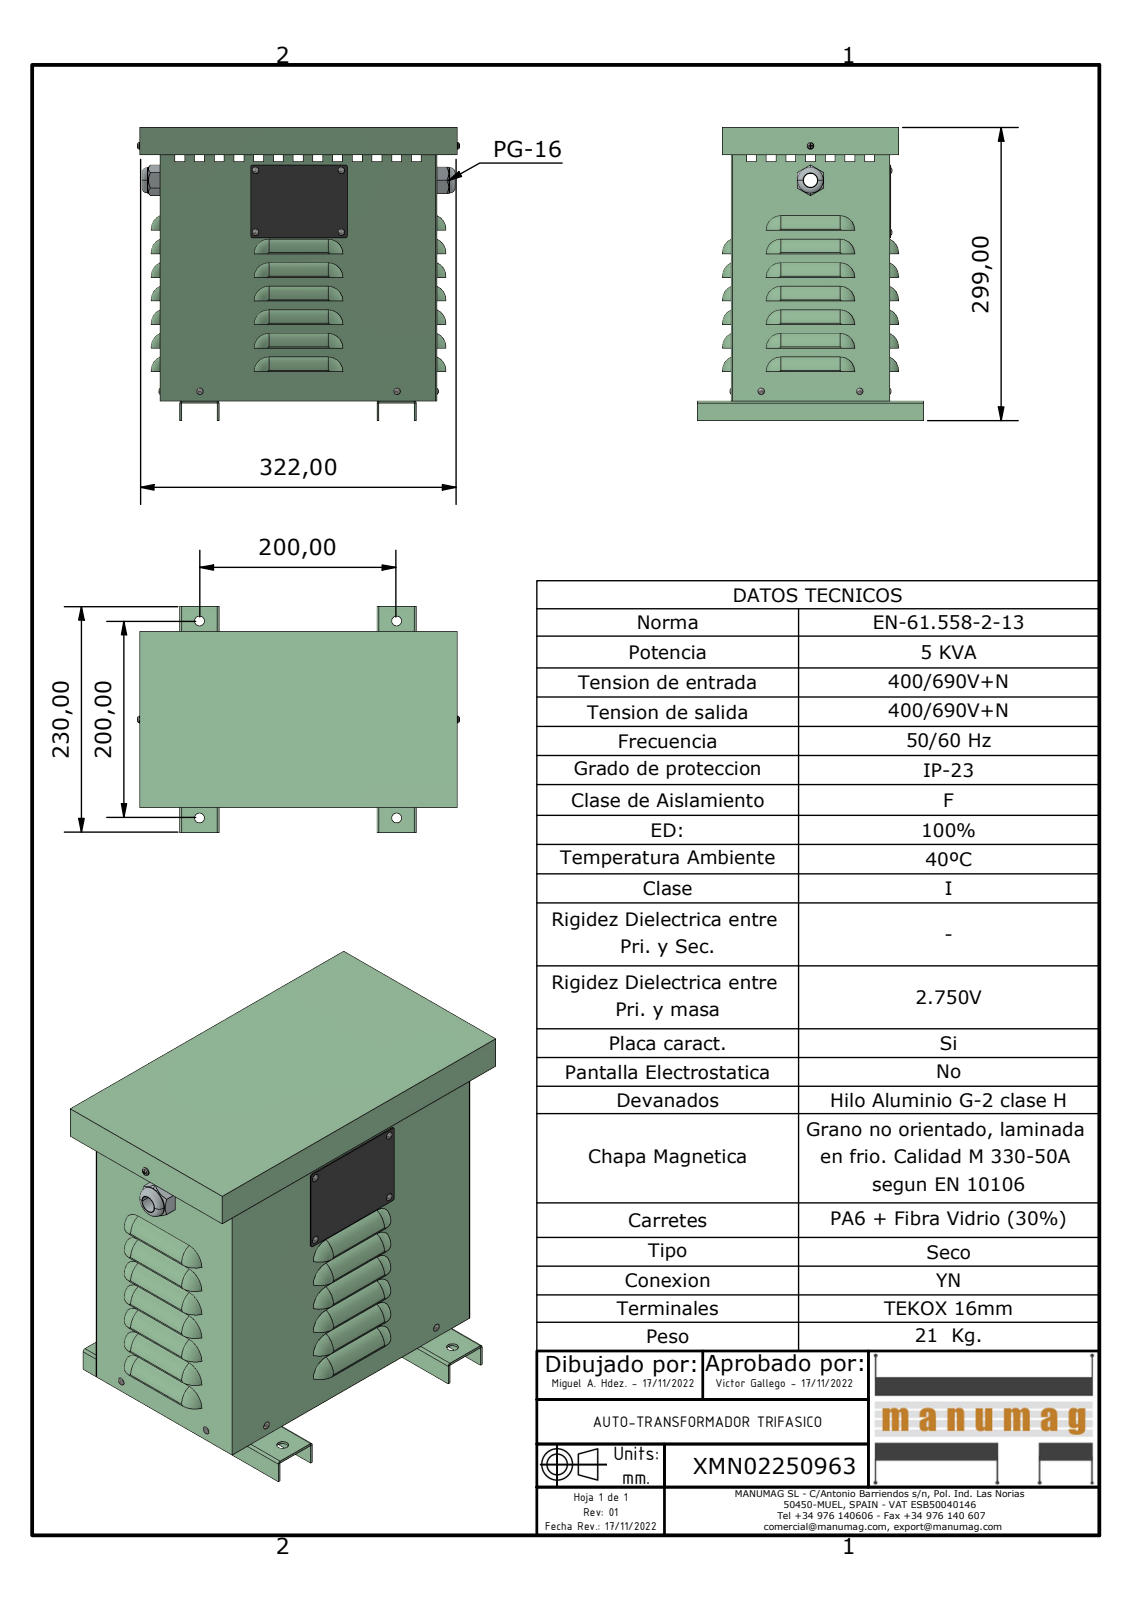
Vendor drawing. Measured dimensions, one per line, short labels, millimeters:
name: XMN02250963; JE003 - JE004 - JE005 NACIONAL CUERPO; JE003 - JE004 - JE005 NACIONAL BASE; PLACA CARACTERISTICAS (+5 more)
written by: Autodesk Inventor 2023 (AUTOMOTIVE_DESIGN)
unit: mm
bodies: 22 solids, 1061 faces (647 planar, 228 cylindrical, 186 other)
size: 327.14 × 299.11 × 230
volume: 789 659 mm³; area: 893 678 mm²
holes: 9× ⌀4, 4× ⌀10, 1× ⌀3, 1× ⌀14, 1× ⌀24
bosses: 8× ⌀3.2, 1× ⌀26, 1× ⌀23, 1× ⌀22.5, 1× ⌀3.5, 1× ⌀3.18
rounds: 26× R7, 26× R14, 26× R15, 18× R1.5, 8× R5, 8× R5.5, 6× R3, 4× R2
face distances: 1.5, 159.5, 277.61, 158, 161, 279.5, 279.11, 278, 9, 168.5
hole spacings: 200, 63, 87, 107.42, 171.57, 216.42, 220.74, 231.99
